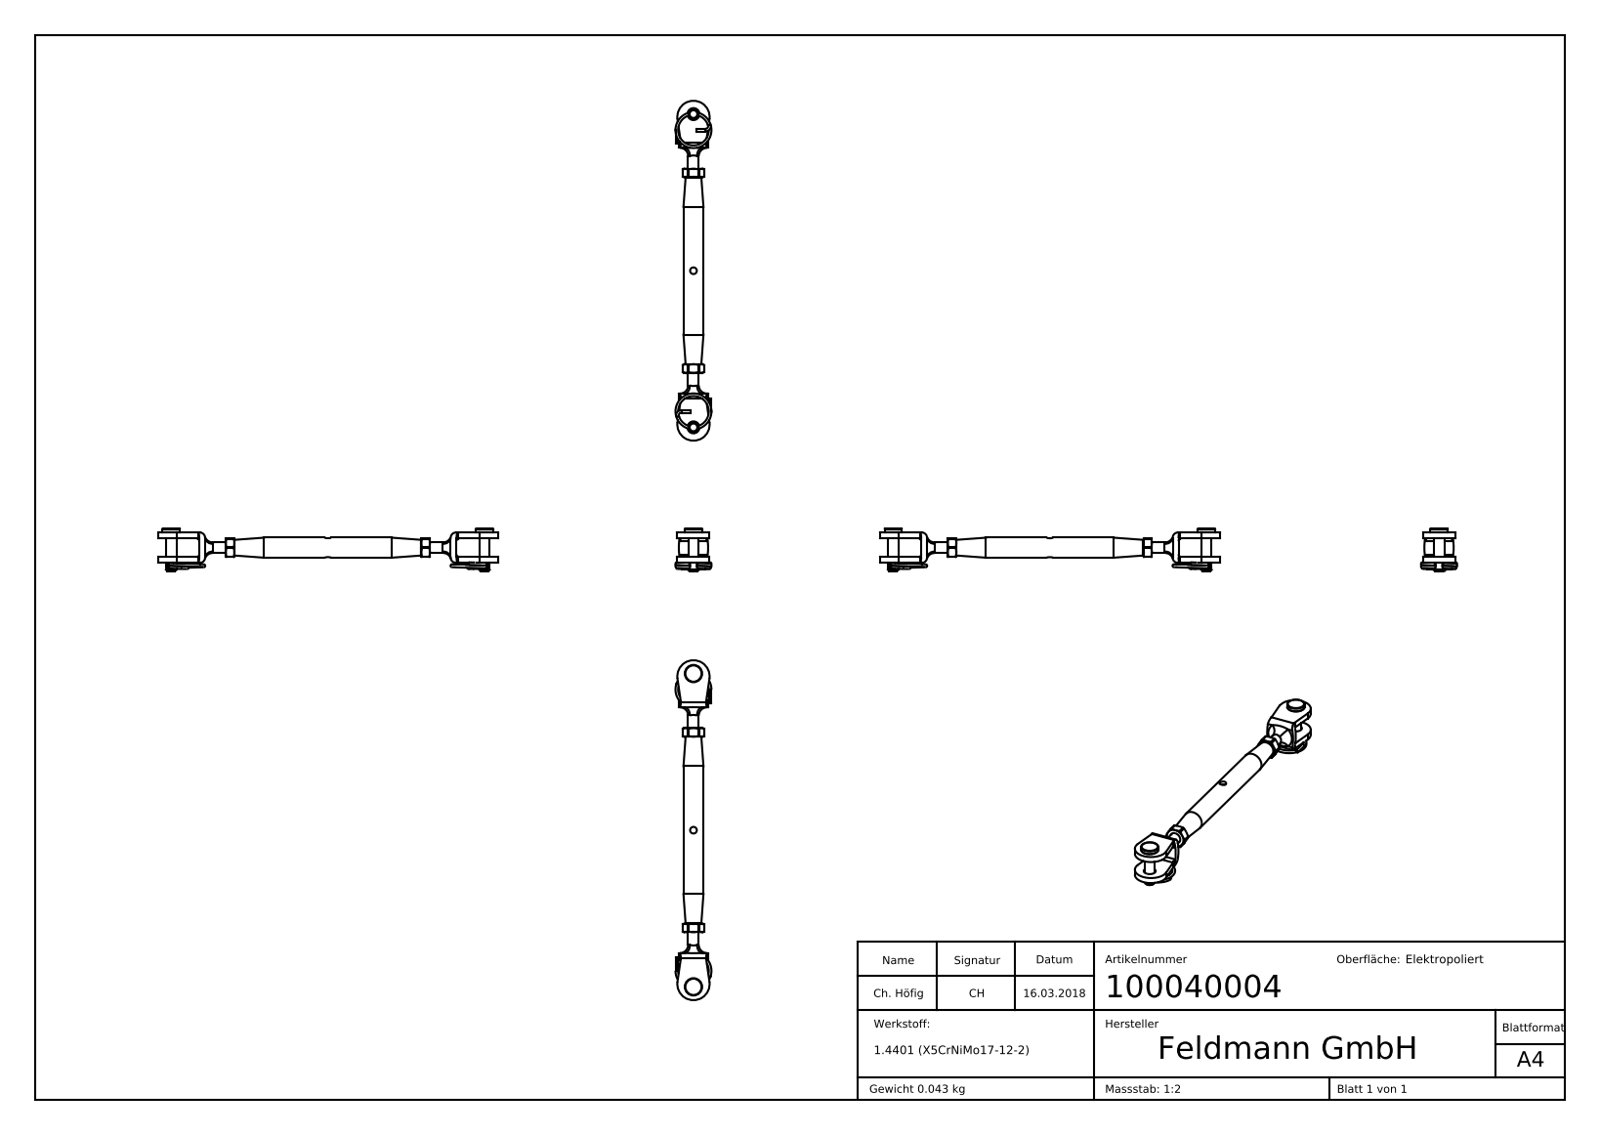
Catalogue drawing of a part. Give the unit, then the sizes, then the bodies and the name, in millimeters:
Units: millimetres
Overall size (bounding box): 127.6 × 16 × 13.5
Round holes (diameter × count): ⌀2.5 ×3, ⌀4.5 ×2, ⌀3.3 ×1, ⌀5 ×1
Round bosses / shafts (diameter × count): ⌀1 ×4, ⌀6.5 ×2, ⌀3.9 ×2, ⌀7.5 ×1, ⌀4 ×1
Partial cylindrical surfaces — rounded edges, fillets, slot ends (radius × count): R0.5 ×6, R0.4 ×4, R1 ×4, R2 ×4, R6.06 ×2, R22.04 ×2, R2.6 ×1
Main face-to-face distances: 2.2, 9.2, 7, 11.4, 4.5, 12.9, 10.7, 3.7, 1.5, 96.6
Hole centre spacings: 58.8, 117.6
Volume: 5 334 mm³ · Surface area: 7 073 mm²
Bodies: 9 solids, 452 faces (138 planar, 122 cylindrical, 192 other)
Part name (STEP PRODUCT): 10004000X Teil1_100040004 Teil1; 10005800X Teil1_100058004 Teil1; 10005800X Teil2_100058004 Teil2; 100040004 (+8 more)
STEP written by: SolidWorks 2015 (CONFIG_CONTROL_DESIGN)
